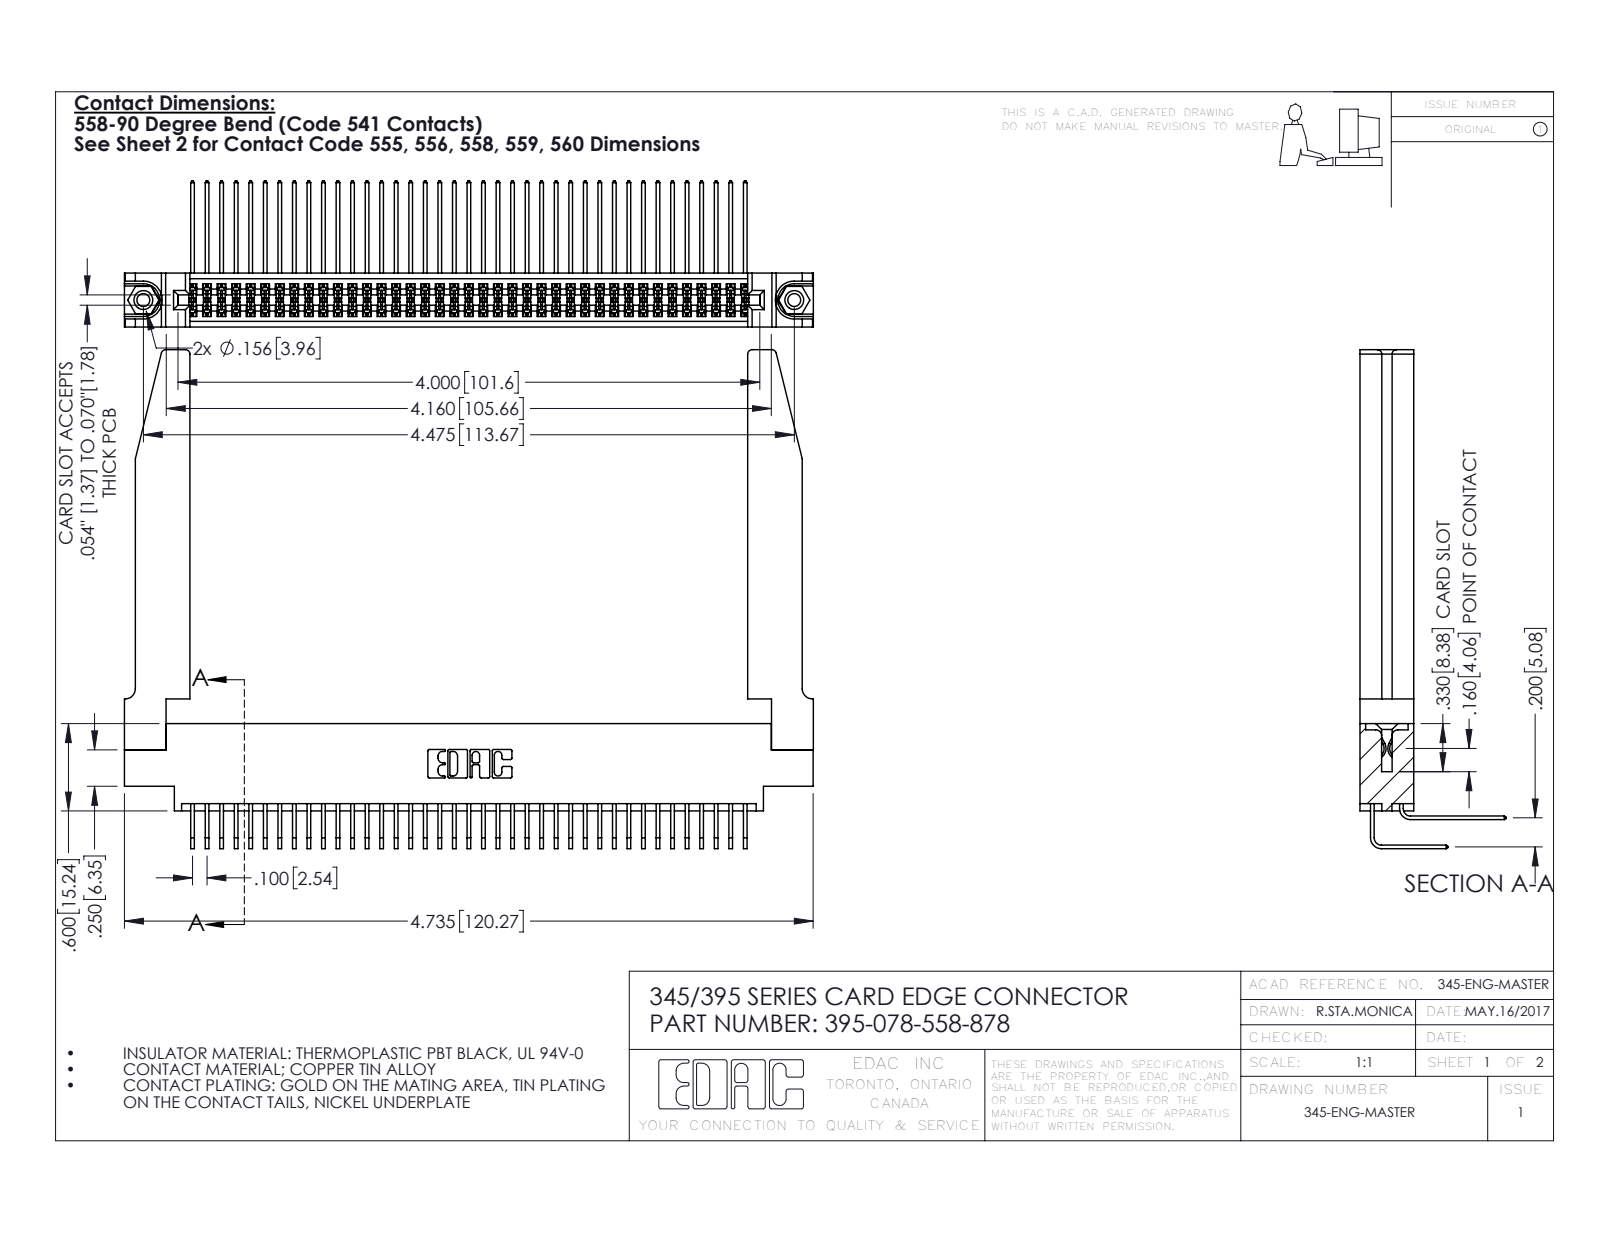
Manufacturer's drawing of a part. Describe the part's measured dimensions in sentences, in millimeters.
The part is named "345-292-001_558 Tail - 2; 345 Part_0.170 Offset - 0.156 Dia-TH; 345-292-001_558 559 Tail - 1; 345-220-078_345-220-078 (+2 more)". Its 3-D file was written by "SolidWorks 2016 (CONFIG_CONTROL_DESIGN)". It is 83 solids with 4420 faces: 2956 planar, 1412 cylindrical and 52 other. Overall it measures 120.3 by 87.1 by 25.5 millimeters. Its volume is 19 760 cubic millimeters and its surface area 26 770 square millimeters. Round holes: 2 of diameter 2.3, 2 of diameter 3.2, 2 of diameter 4, 1 of diameter 1.6. Round bosses or shafts: 2 of diameter 3.9. Partial cylindrical surfaces (rounded edges, fillets, slot ends): 118 of radius 0.2, 22 of radius 0.3, 8 of radius 0.8, 6 of radius 0.2, 6 of radius 0.8, 3 of radius 0.7, 2 of radius 0.4, 2 of radius 0.5. The main face-to-face distances are 9.4, 1.8, 7.6, 5.1, 2.5, 6.9, 0.6, 5.7, 4.4, 3.8. The hole center spacings are 6.9, 107.7, 113.7.
